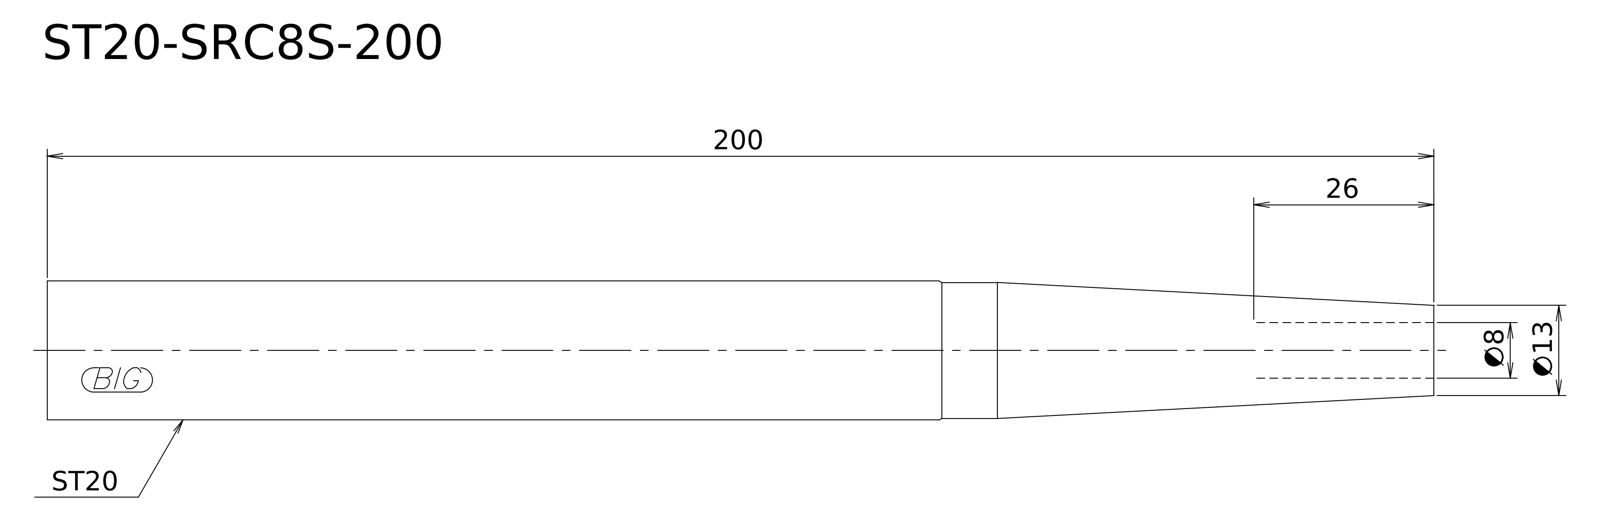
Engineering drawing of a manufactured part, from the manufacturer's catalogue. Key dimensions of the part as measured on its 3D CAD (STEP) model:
STEP written by: Kubotek KeyCreator V8.5.1 (14335) (CONFIG_CONTROL_DESIGN)
Units: millimetres
Bodies: 1 solid, 6 faces (2 planar, 2 cylindrical, 2 other)
Overall size (bounding box): 200 × 20 × 20
Volume: 56 267 mm³ · Surface area: 12 279 mm²
Round bosses / shafts (diameter × count): ⌀20 ×1, ⌀19.6 ×1
Main face-to-face distances: 200
